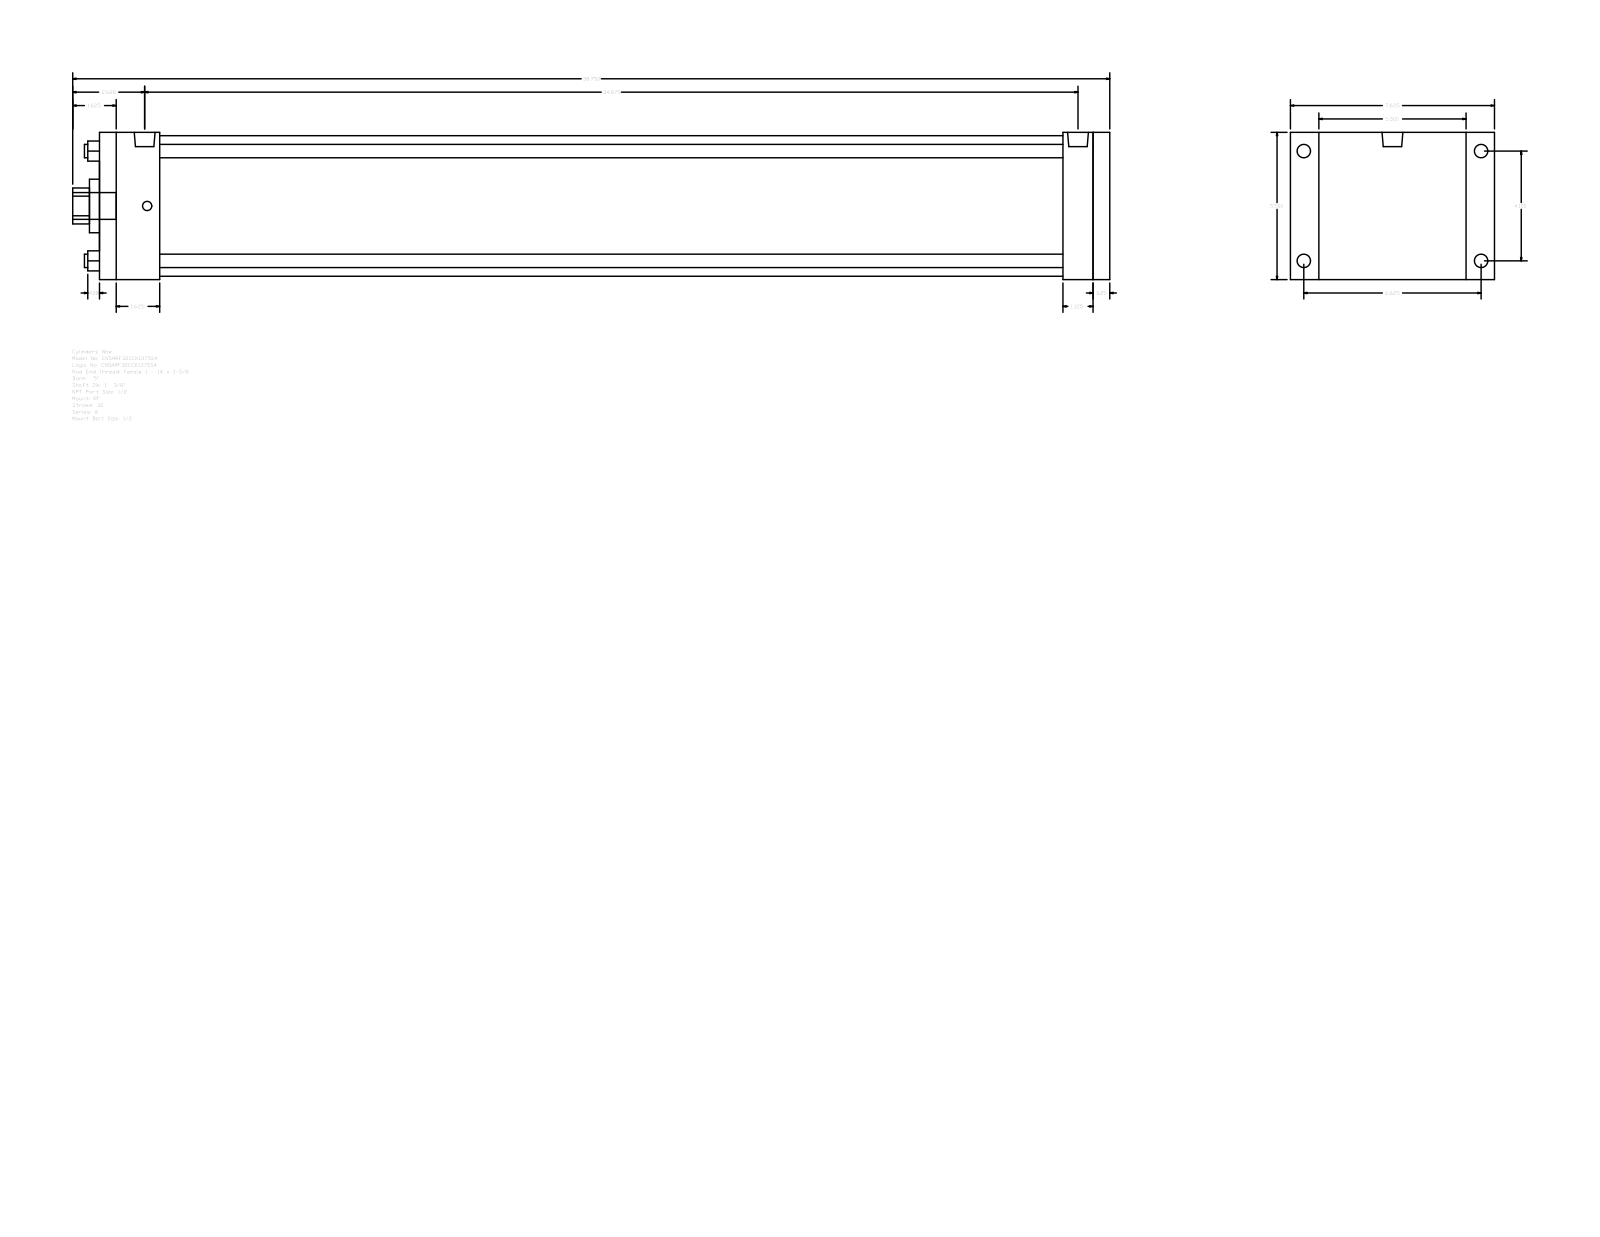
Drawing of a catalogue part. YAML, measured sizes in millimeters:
part_name: "A_RF__0500_1.375"
step_written_by: "GSSL Pune (CONFIG_CONTROL_DESIGN)"
units: millimeters
bodies: {solids: 0, faces: 92, planar: 64, cylindrical: 28, other: 0}
overall_size: [984.25, 193.68, 139.7]
round_holes:
  - {diameter: 12.7, count: 4}
  - {diameter: 34.92, count: 1}
  - {diameter: 50.8, count: 1}
  - {diameter: 133.35, count: 1}
round_bosses_or_shafts:
  - {diameter: 12.7, count: 4}
  - {diameter: 8.73, count: 4}
  - {diameter: 19.77, count: 2}
  - {diameter: 25.4, count: 1}
partial_cylinders:
  - {radius: 17.06, count: 1}
face_to_face_distances: [139.7, 958.85, 15.87, 942.98, 28.58, 57.15, 885.83, 901.7, 914.4, 857.25]
hole_center_spacings: [73.64, 104.14, 147.28]
